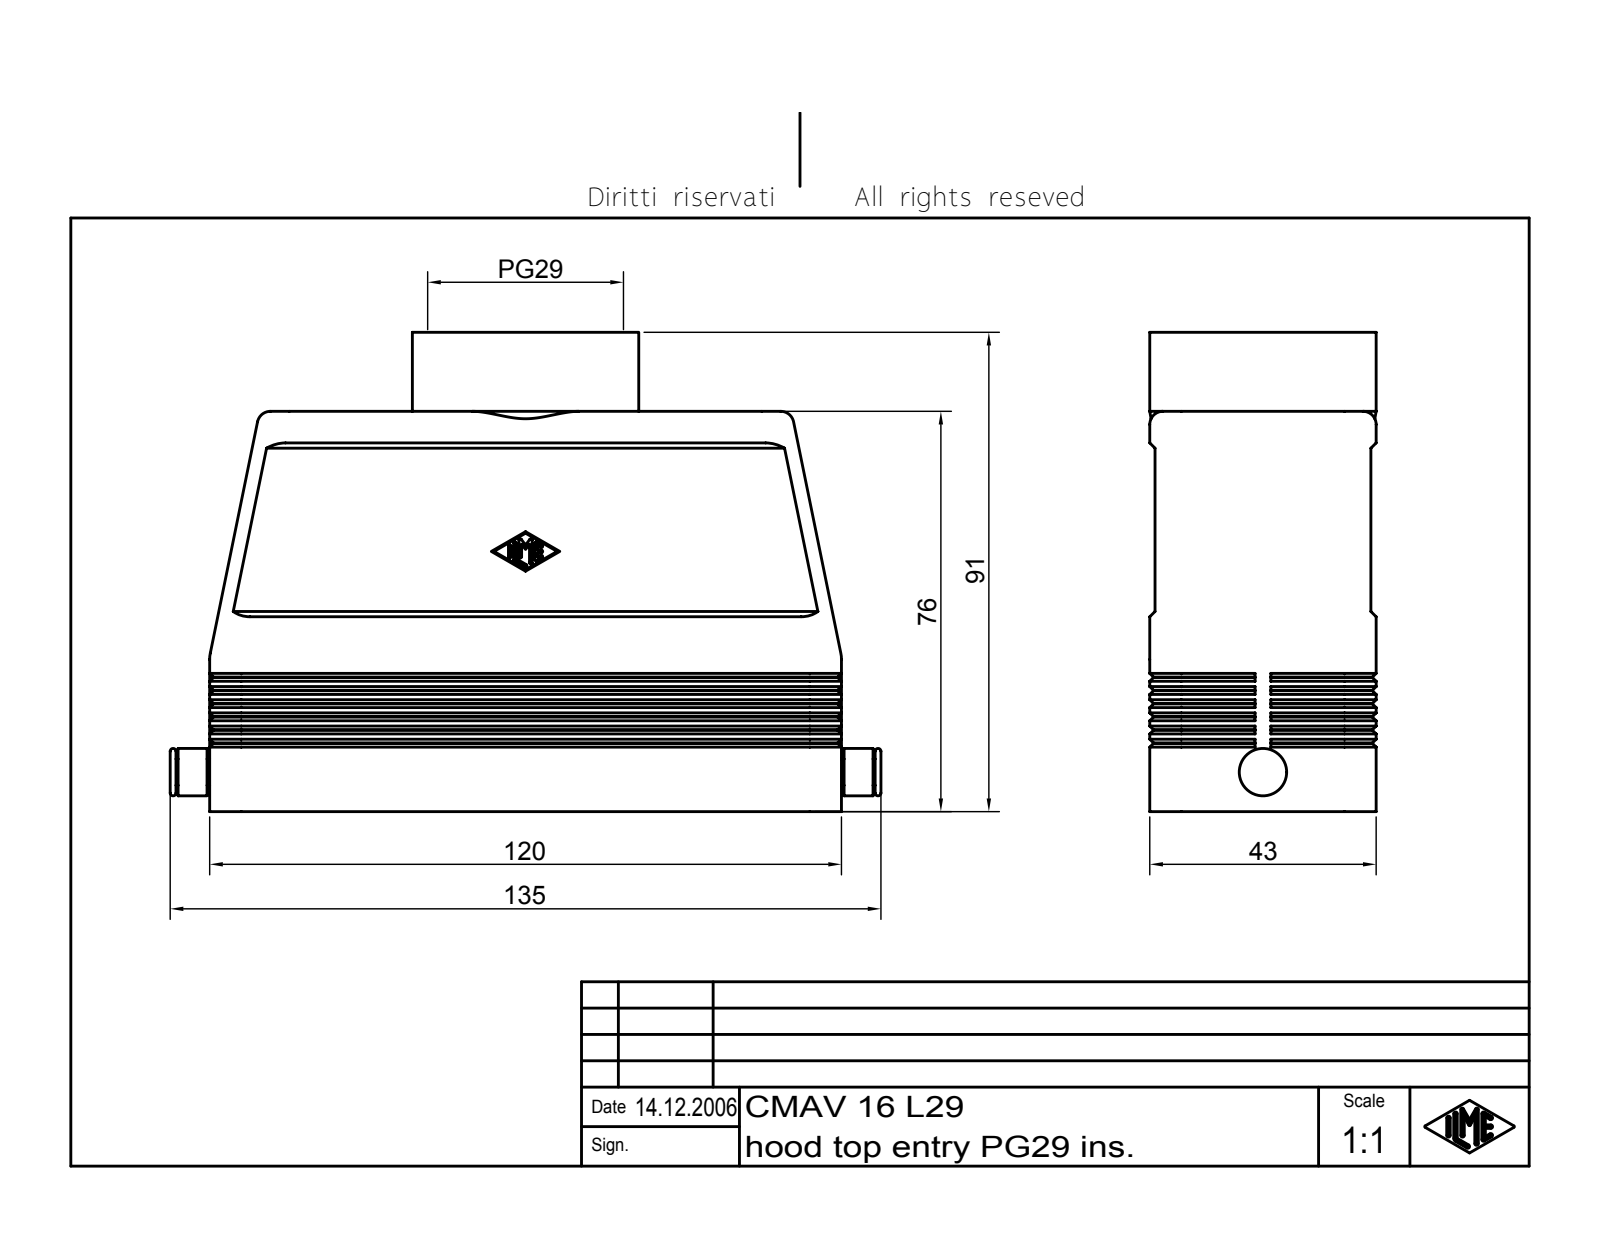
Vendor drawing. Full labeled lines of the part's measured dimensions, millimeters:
Part name (STEP PRODUCT): CH Tüllengehäuse für einen Einsatz Teil 6
STEP written by: Autodesk Inventor 7 (AUTOMOTIVE_DESIGN)
Units: millimetres
Bodies: 1 solid, 525 faces (193 planar, 130 cylindrical, 202 other)
Overall size (bounding box): 135 × 91 × 43
Volume: 89 355 mm³ · Surface area: 57 622 mm²
Round holes (diameter × count): ⌀33.48 ×1, ⌀35.48 ×1
Round bosses / shafts (diameter × count): ⌀43 ×1, ⌀34.48 ×1, ⌀9 ×1, ⌀5 ×1
Partial cylindrical surfaces — rounded edges, fillets, slot ends (radius × count): R0.25 ×14, R6 ×10, R2 ×4, R2.5 ×4, R3 ×4, R5.3 ×2
Main face-to-face distances: 3, 37, 40, 1, 2, 42, 39, 43, 41, 9
